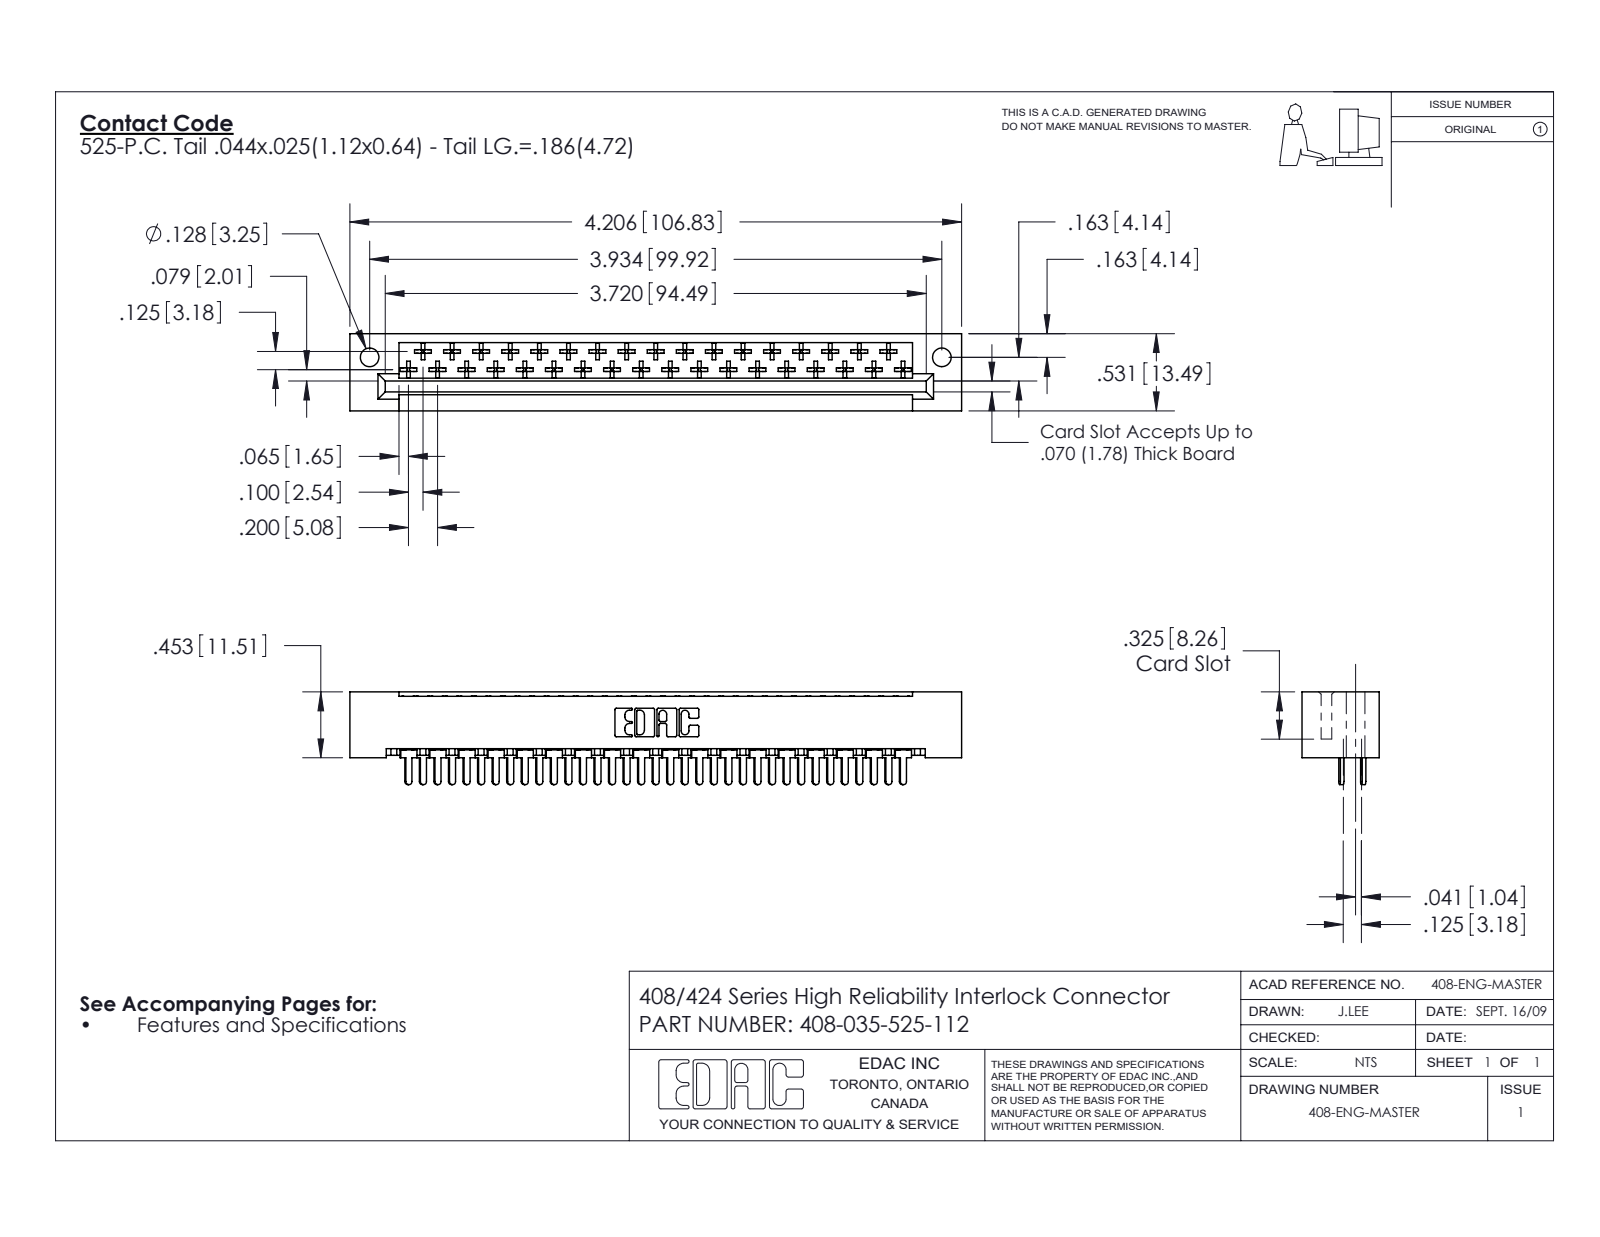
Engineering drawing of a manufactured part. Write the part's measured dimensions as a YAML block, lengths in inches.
part_name: "408-290-001_408-290-125 - Bottom; 408-290-001_408-290-125 - Top; 408 Part_035 - 1; 408-035-525-112"
step_written_by: "SolidWorks 2016 (CONFIG_CONTROL_DESIGN)"
units: inches
bodies: {solids: 36, faces: 2052, planar: 1549, cylindrical: 363, other: 140}
overall_size: [4.206, 0.638, 0.531]
volume: 0.748
surface_area: 22.68
round_holes:
  - {diameter: 0.128, count: 2}
partial_cylinders:
  - {radius: 0.01, count: 210}
  - {radius: 0.02, count: 37}
  - {radius: 0.022, count: 35}
  - {radius: 0.01, count: 22}
  - {radius: 0.007, count: 6}
  - {radius: 0.031, count: 6}
  - {radius: 0.026, count: 3}
face_to_face_distances: [0.531, 0.025, 0.125, 0.1, 0.025, 0.4, 0.272, 0.235, 0.259, 0.296]
hole_center_spacings: [3.934]
